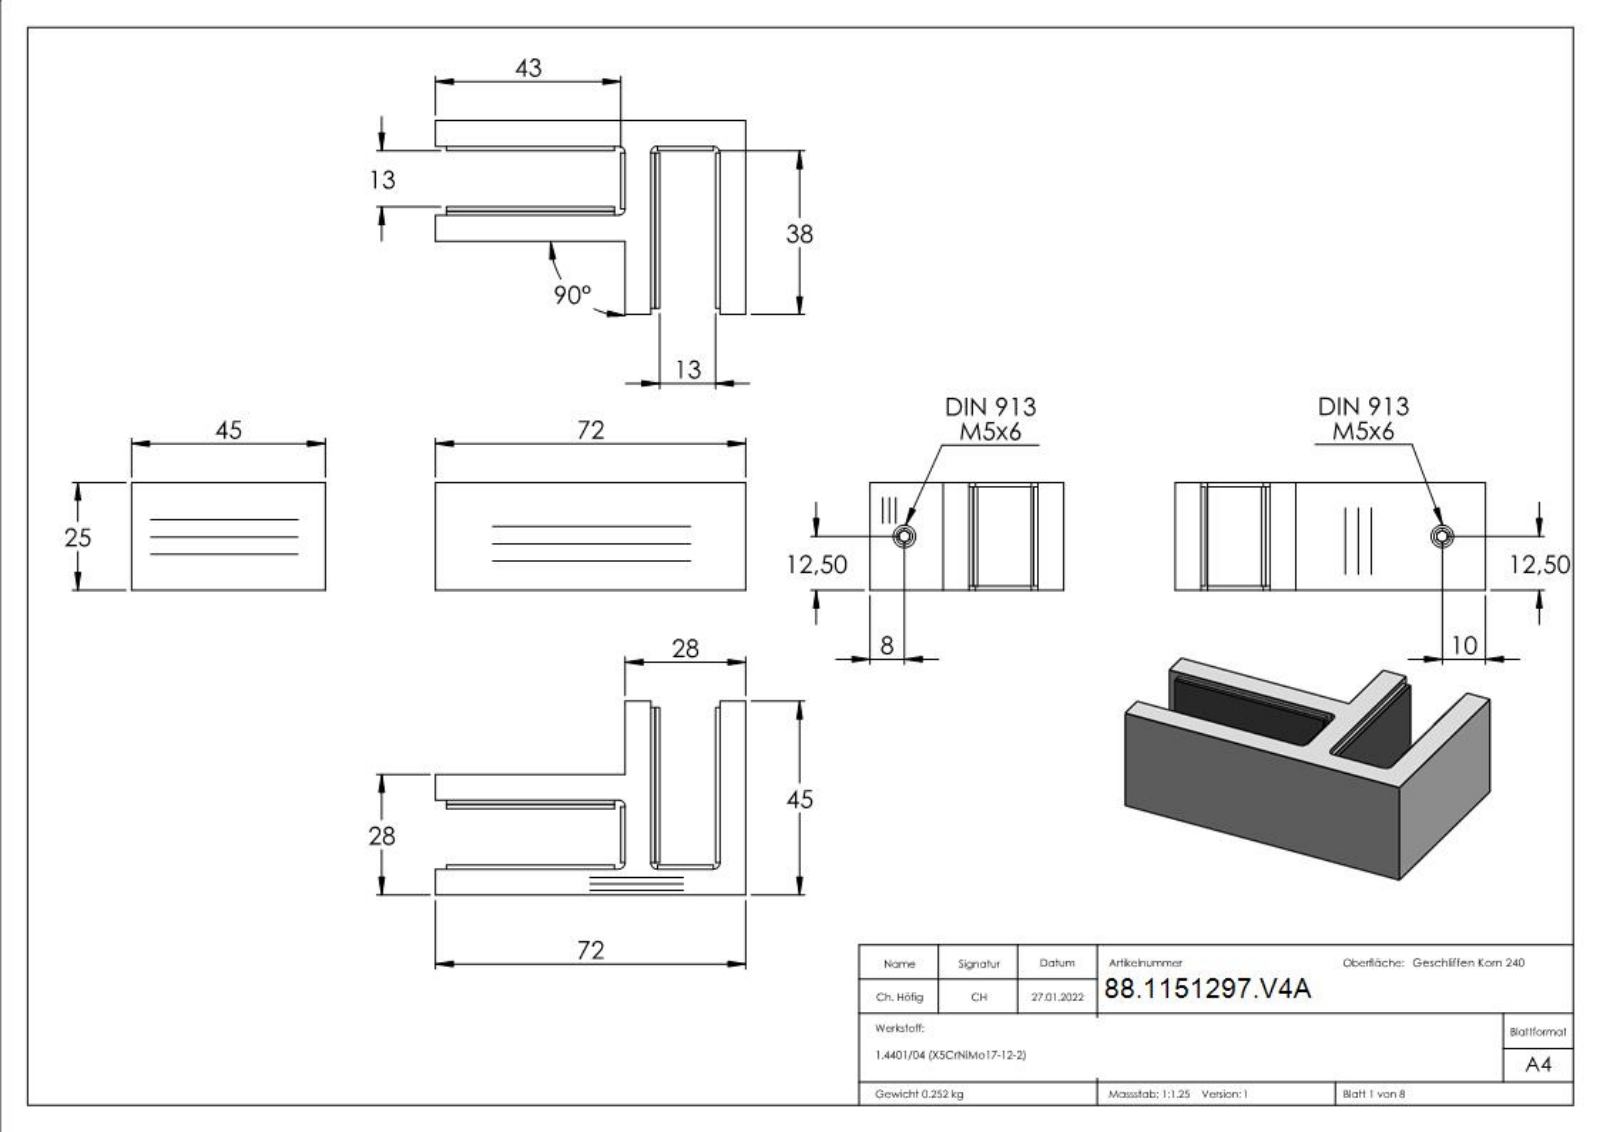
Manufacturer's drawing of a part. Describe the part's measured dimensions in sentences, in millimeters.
The part is named "51297-V4A Teil6; 51297-V4A Teil4; 51297-V4A Teil1; 51297-V4A Teil6_51297-V4A Teil6 (+8 more)". Its 3-D file was written by "SolidWorks 2018 (CONFIG_CONTROL_DESIGN)". It is 11 solids with 428 faces: 280 planar, 20 cylindrical and 128 other. Overall it measures 70000 by 5000 by 5000 millimeters. Its volume is 34 908 cubic millimeters and its surface area 25 091 square millimeters. Round holes: 2 of diameter 4.2. Round bosses or shafts: 2 of diameter 5. Partial cylindrical surfaces (rounded edges, fillets, slot ends): 8 of radius 0.5, 4 of radius 1.5. The main face-to-face distances are 1, 15, 22, 6, 21, 7, 14, 16, 28, 8.
